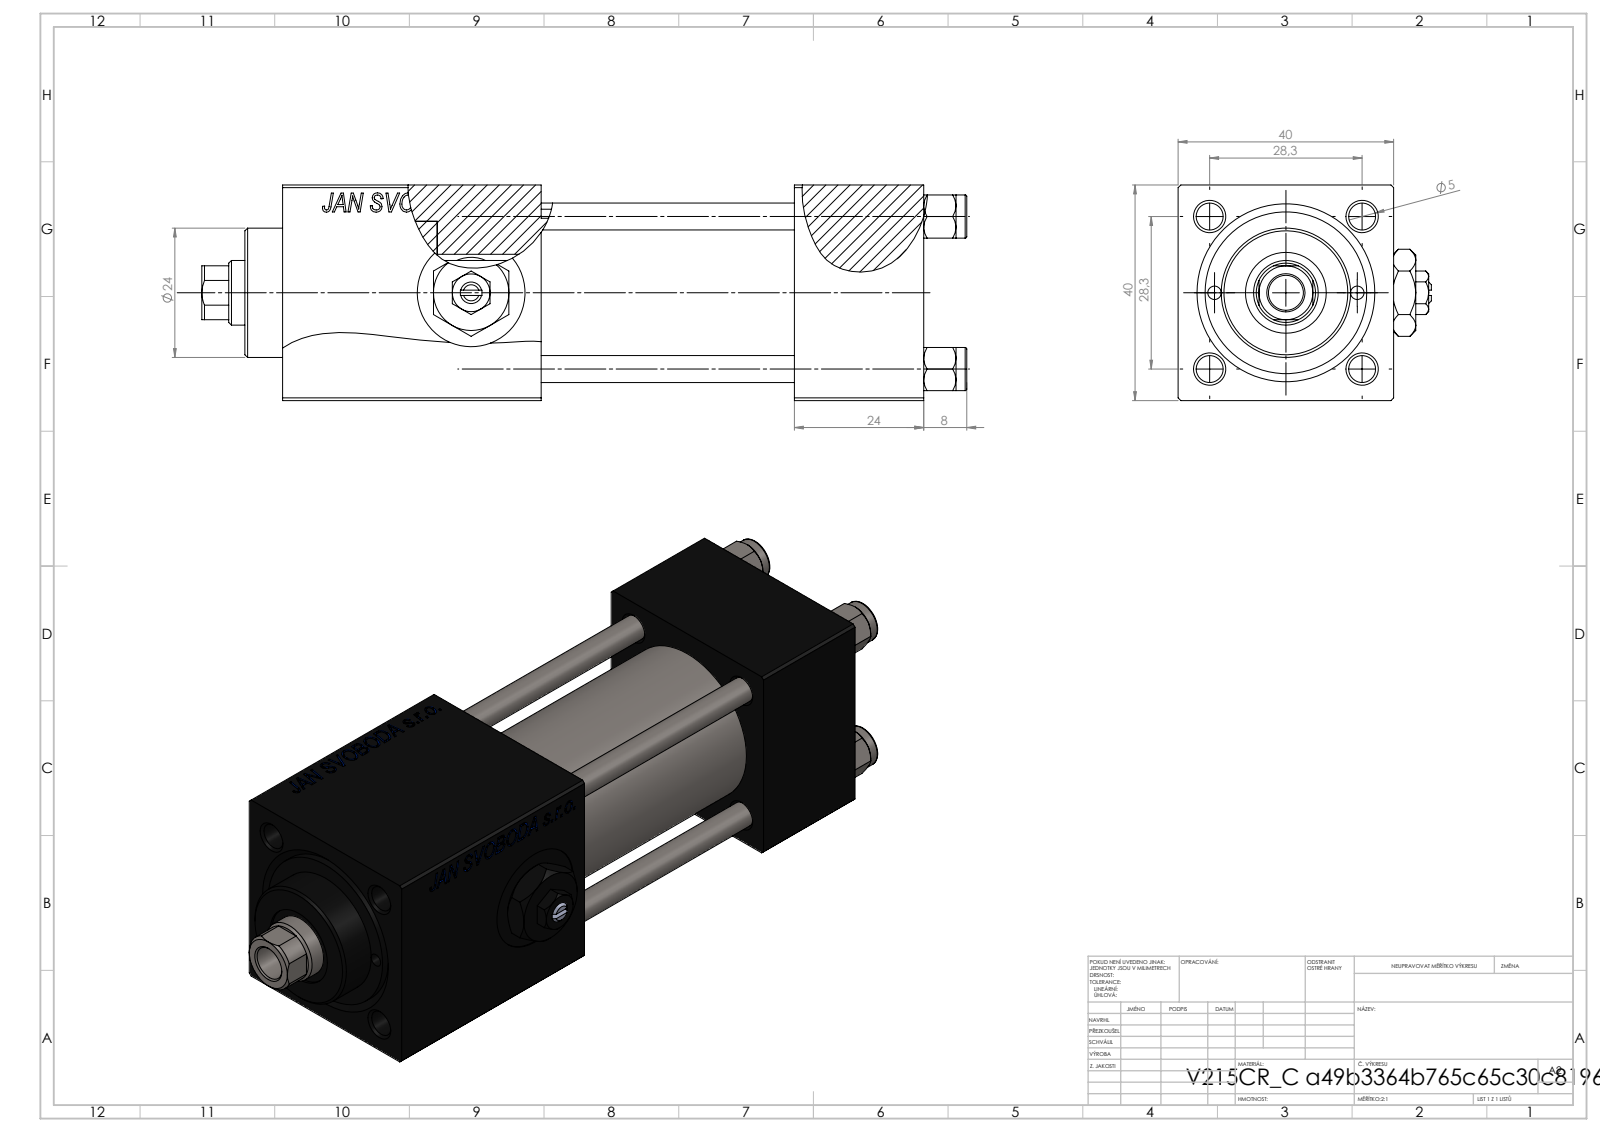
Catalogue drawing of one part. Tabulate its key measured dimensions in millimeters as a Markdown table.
| quantity | value |
| --- | --- |
| part name | V215_VC_A; V215CR_C_TYCINKA; V215CR_C_Body; NUT_M5_C (+2 more) |
| STEP written by | SolidWorks 2019 (CONFIG_CONTROL_DESIGN) |
| units | millimeters |
| bodies | 12 solids, 1201 faces (551 planar, 94 cylindrical, 556 other) |
| overall size | 142 × 47 × 40 |
| volume | 141 689 mm³ |
| surface area | 55 264 mm² |
| round holes (diameter × count) | 5 × 4, 20 × 3, 2.5 × 2, 7 × 2, 13.16 × 2, 6.5 × 1, 12 × 1, 15 × 1, 25 × 1, 30 × 1 |
| round bosses / shafts (diameter × count) | 8 × 4, 31 × 1, 24 × 1 |
| partial cylindrical surfaces (radius × count) | 5.5 × 1 |
| main face-to-face distances | 40, 24, 90.3, 66.3, 48, 47, 71, 19.3, 119, 95 |
| hole center spacings | 14.18, 20.01, 28.3, 30.84, 13.25, 40.02, 26.5, 72 |
